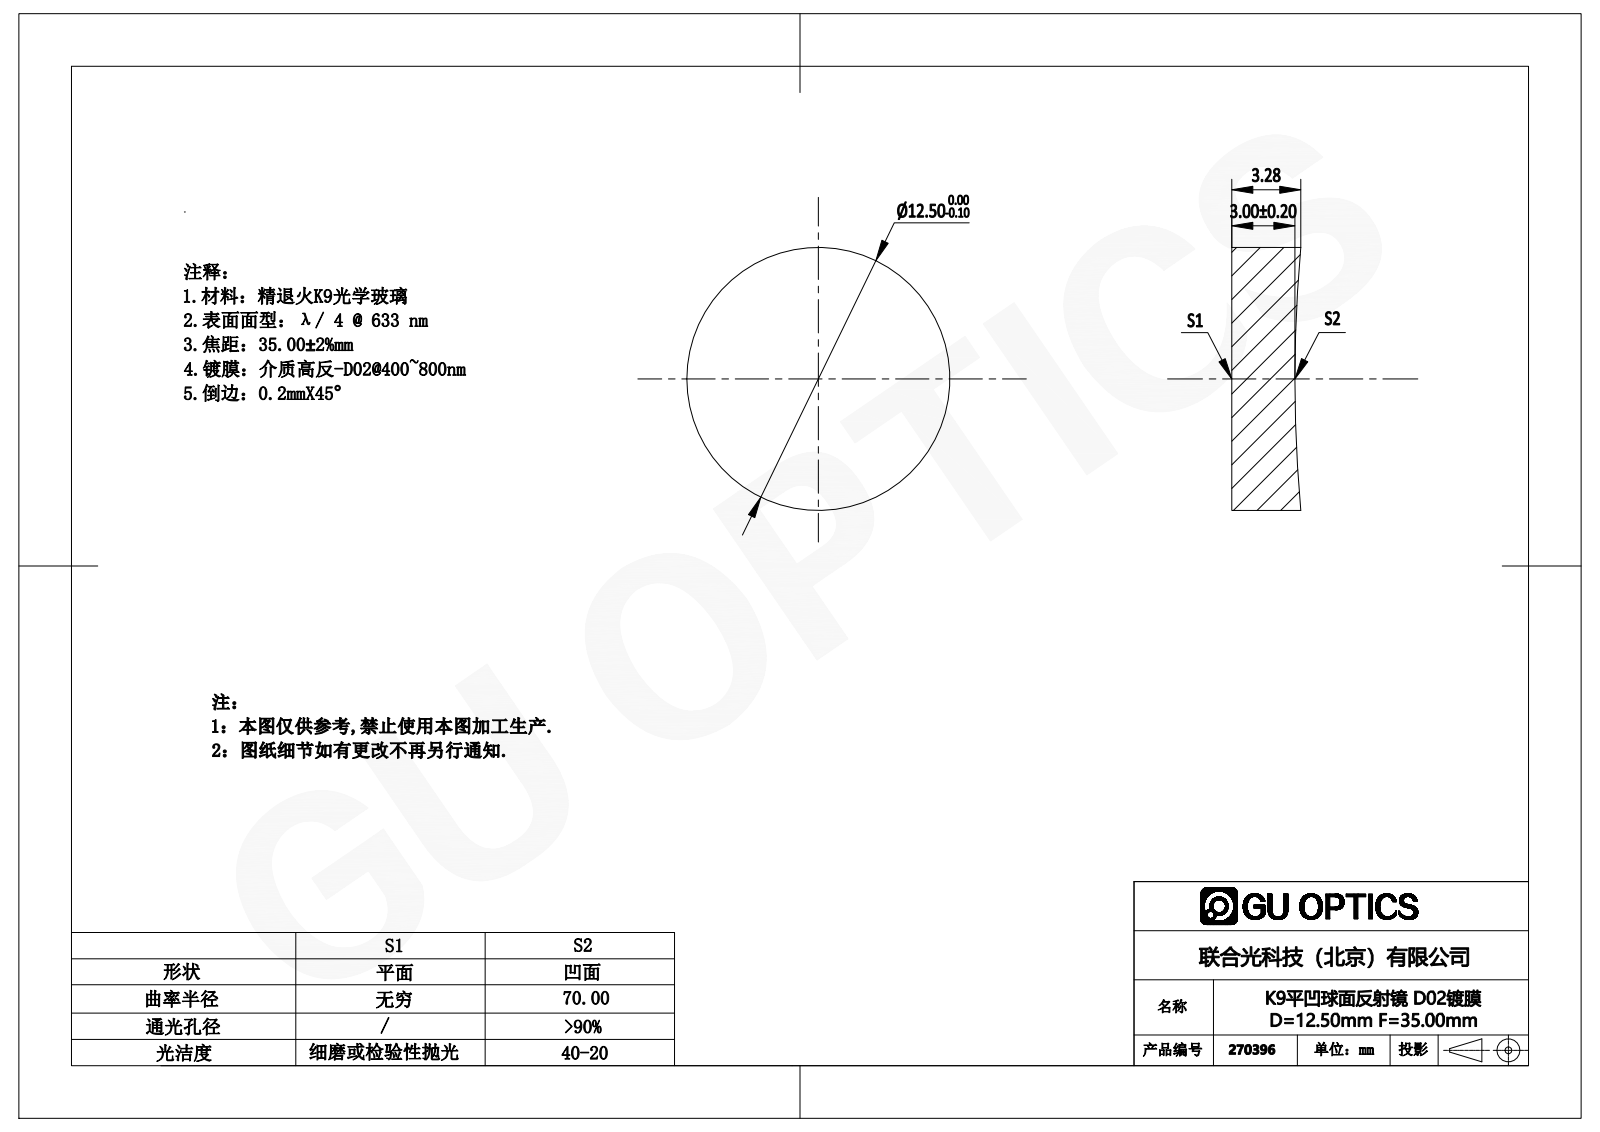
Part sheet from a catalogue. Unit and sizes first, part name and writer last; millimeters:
Units: millimetres
Overall size (bounding box): 12.5 × 12.5 × 3.28
Round bosses / shafts (diameter × count): ⌀12.5 ×1
Volume: 385 mm³ · Surface area: 374 mm²
Bodies: 1 solid, 5 faces (1 planar, 2 cylindrical, 2 other)
Part name (STEP PRODUCT): 270006
STEP written by: SolidWorks 2016 (AUTOMOTIVE_DESIGN)
